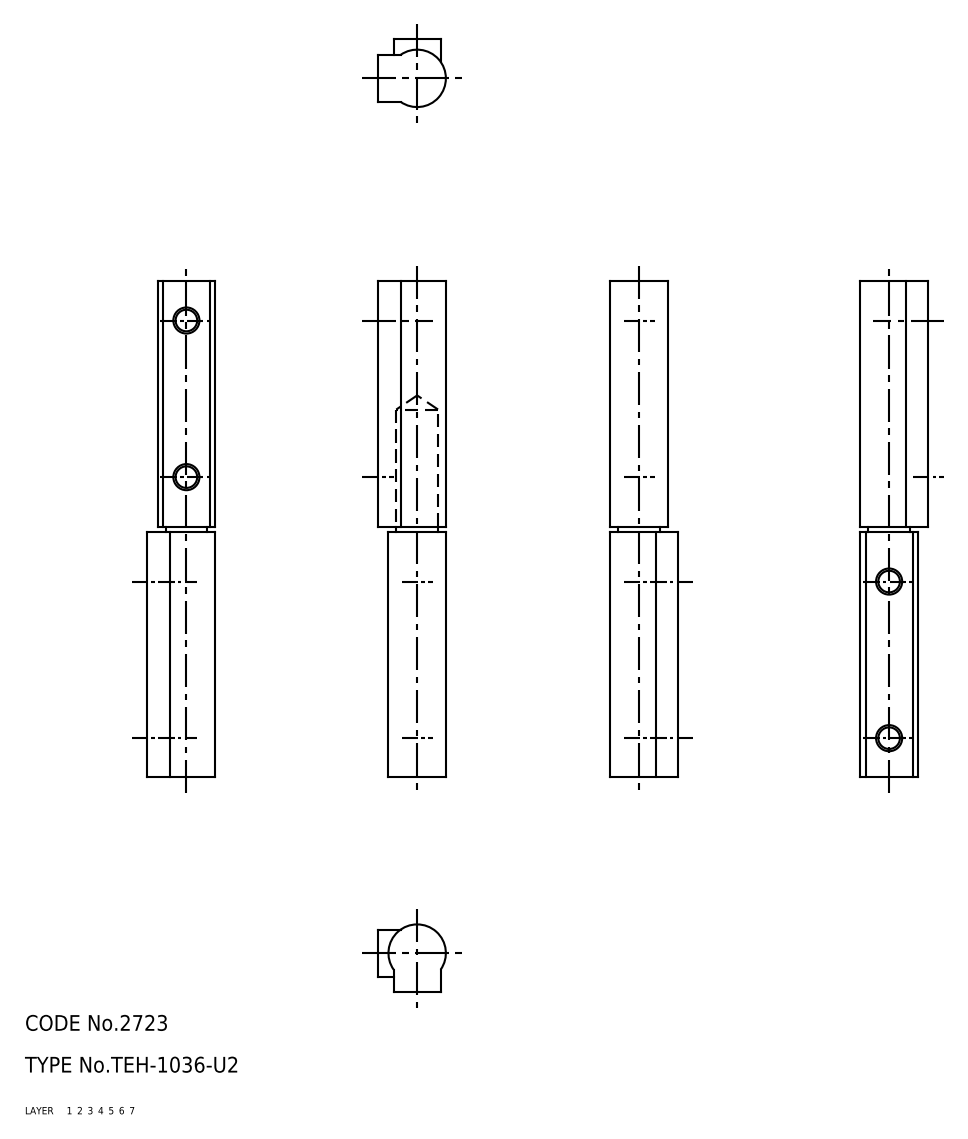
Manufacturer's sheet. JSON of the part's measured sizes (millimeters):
{"part_name": "hinge pieces_B; hinge pieces_A; TEH_1036_U2_4199_36", "step_written_by": "CADfix (AUTOMOTIVE_DESIGN)", "units": "millimeters", "bodies": {"solids": 2, "faces": 32, "planar": 0, "cylindrical": 0, "other": 32}, "overall_size": [95, 13, 13], "volume_mm3": 10652, "surface_area_mm2": 5993}
